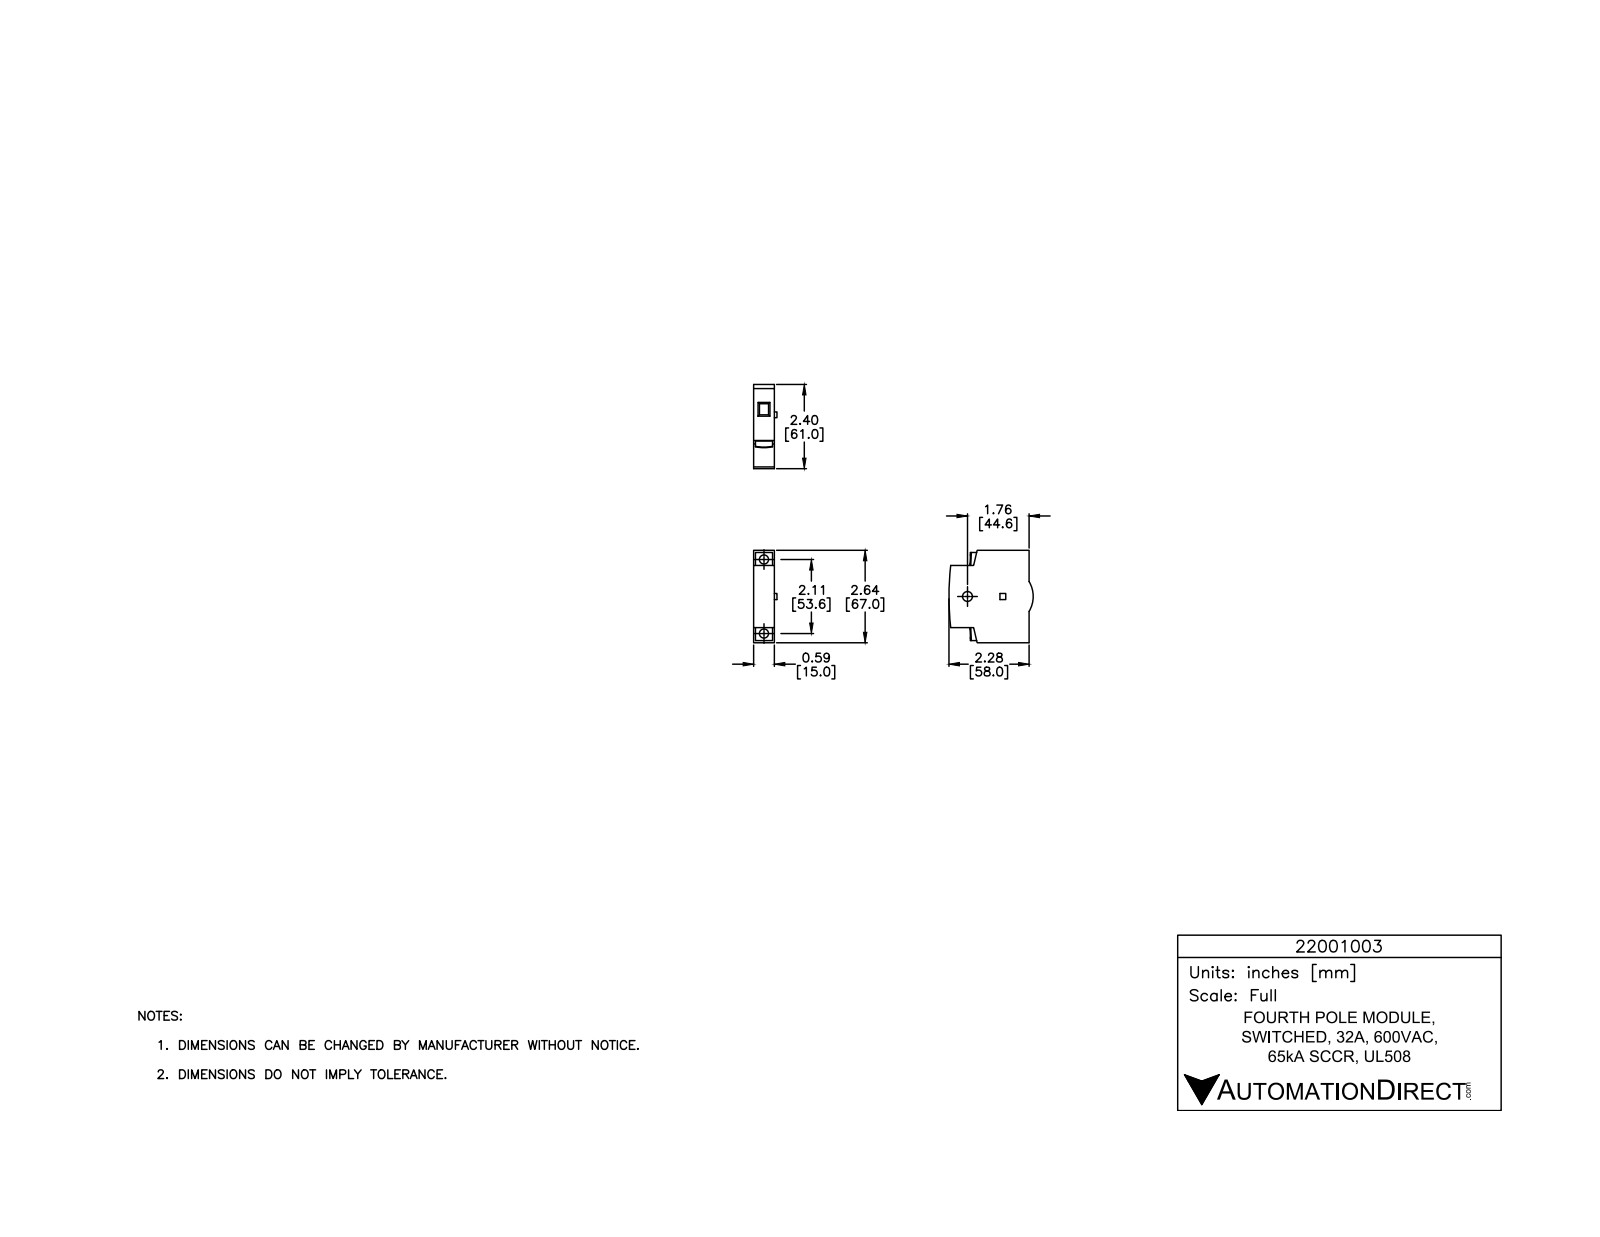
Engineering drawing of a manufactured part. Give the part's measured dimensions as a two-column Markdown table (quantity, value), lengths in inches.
| quantity | value |
| --- | --- |
| part name | 22001003-UL |
| STEP written by | SolidWorks 2021 (CONFIG_CONTROL_DESIGN) |
| units | inches |
| bodies | 1 solid, 61 faces (46 planar, 11 cylindrical, 4 other) |
| overall size | 2.638 × 2.402 × 0.665 |
| volume | 3.141 in³ |
| surface area | 18.13 in² |
| round holes (diameter × count) | 0.26 × 2, 0.283 × 1 |
| partial cylindrical surfaces (radius × count) | 0.827 × 1, 7.874 × 1 |
| main face-to-face distances | 0.591, 2.638, 0.433, 2.205, 1.772, 0.063, 2.575, 0.37, 2.142, 0.051 |
| hole center spacings | 2.11 |
